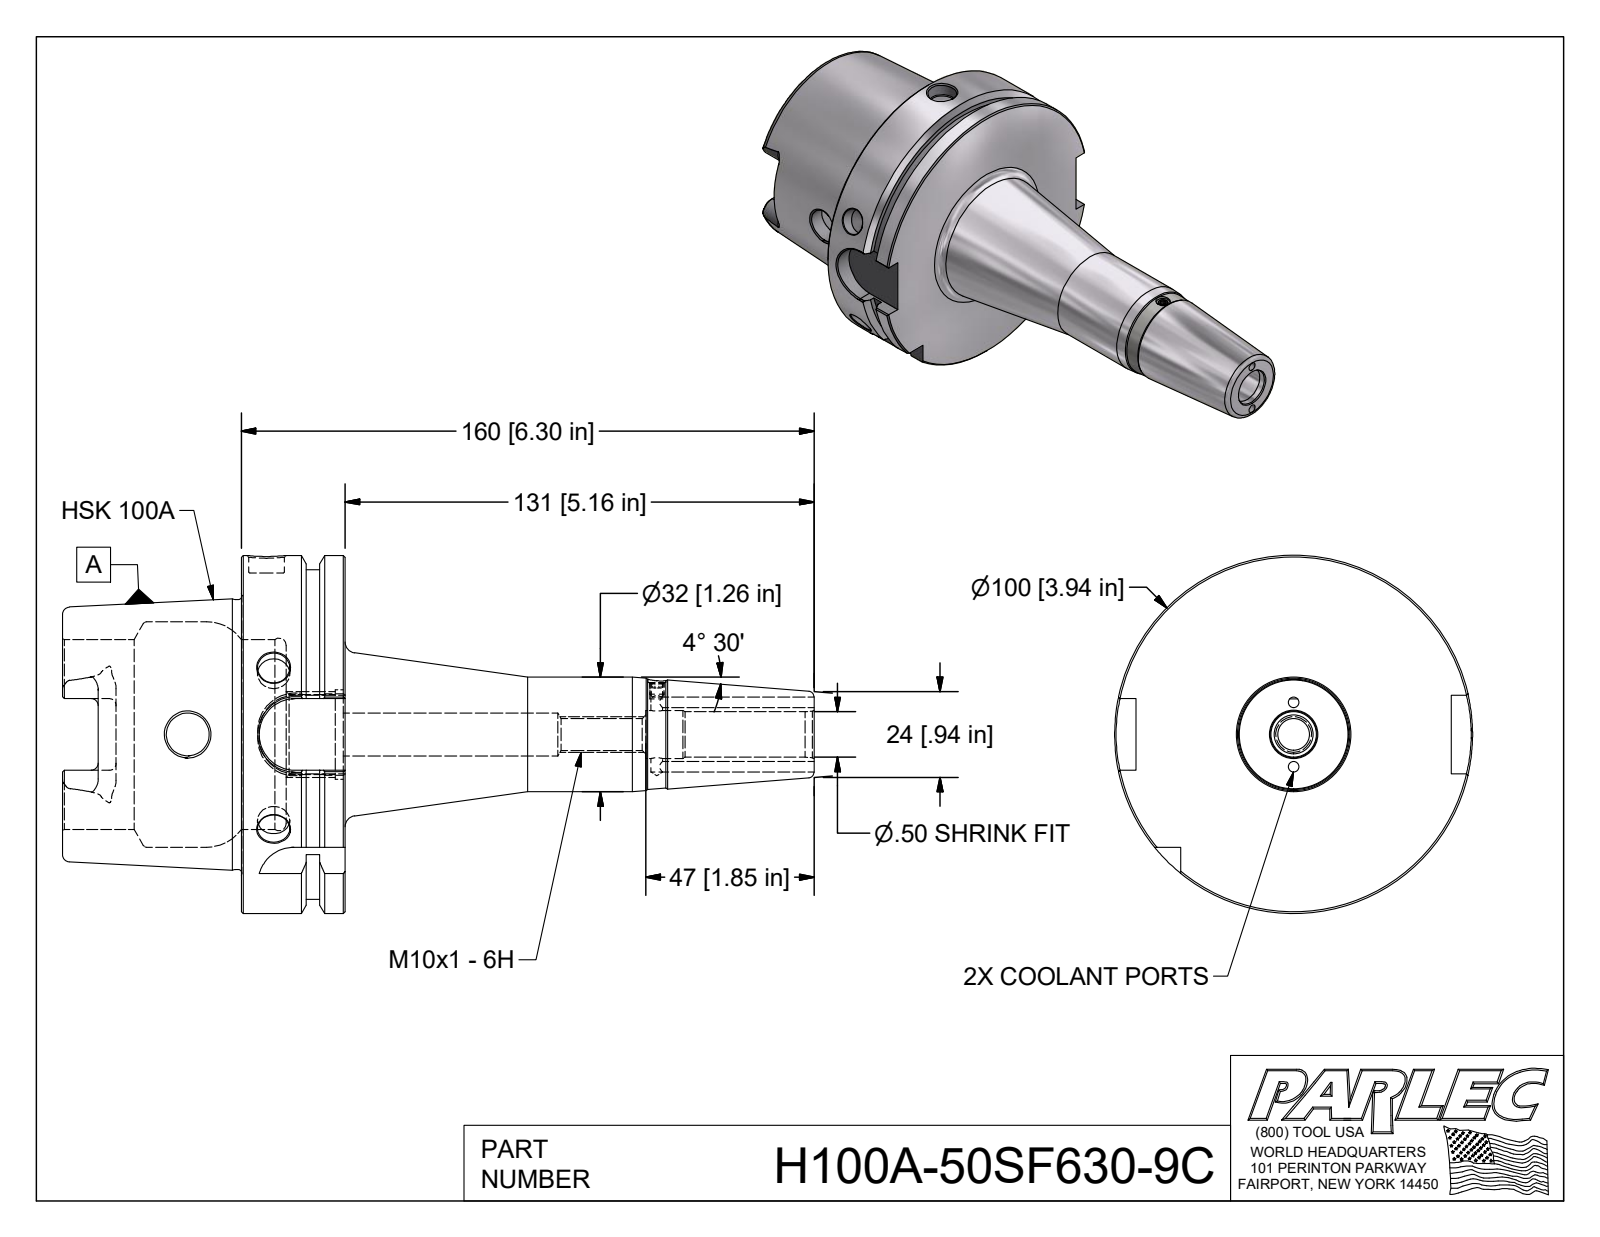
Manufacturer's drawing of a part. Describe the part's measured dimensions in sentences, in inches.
Its 3-D file was written by "Autodesk Inventor 2018 (AUTOMOTIVE_DESIGN)". It is 1 solid with 155 faces: 49 planar, 42 cylindrical and 64 other. Overall it measures 8.268 by 3.937 by 3.937 inches. Its volume is 21.72 cubic inches and its surface area 105.4 square inches. Round holes: 2 of diameter 0.118, 2 of diameter 0.354, 2 of diameter 0.472, 1 of diameter 0.128, 1 of diameter 0.197, 1 of diameter 0.351, 1 of diameter 0.394, 1 of diameter 0.499, 1 of diameter 0.529, 1 of diameter 0.881, 1 of diameter 0.985, 1 of diameter 2.087. Round bosses or shafts: 1 of diameter 3.937, 1 of diameter 3.622, 1 of diameter 2.967, 1 of diameter 1.26. Partial cylindrical surfaces (rounded edges, fillets, slot ends): 6 of radius 0.079, 4 of radius 0.192, 4 of radius 0.394. The main face-to-face distances are 1.142, 0.492, 0.65, 1.969, 2.461, 3.11, 3.465, 2.83, 0.861, 0.369. The hole center spacings are 0.354, 0.708, 4.294.
